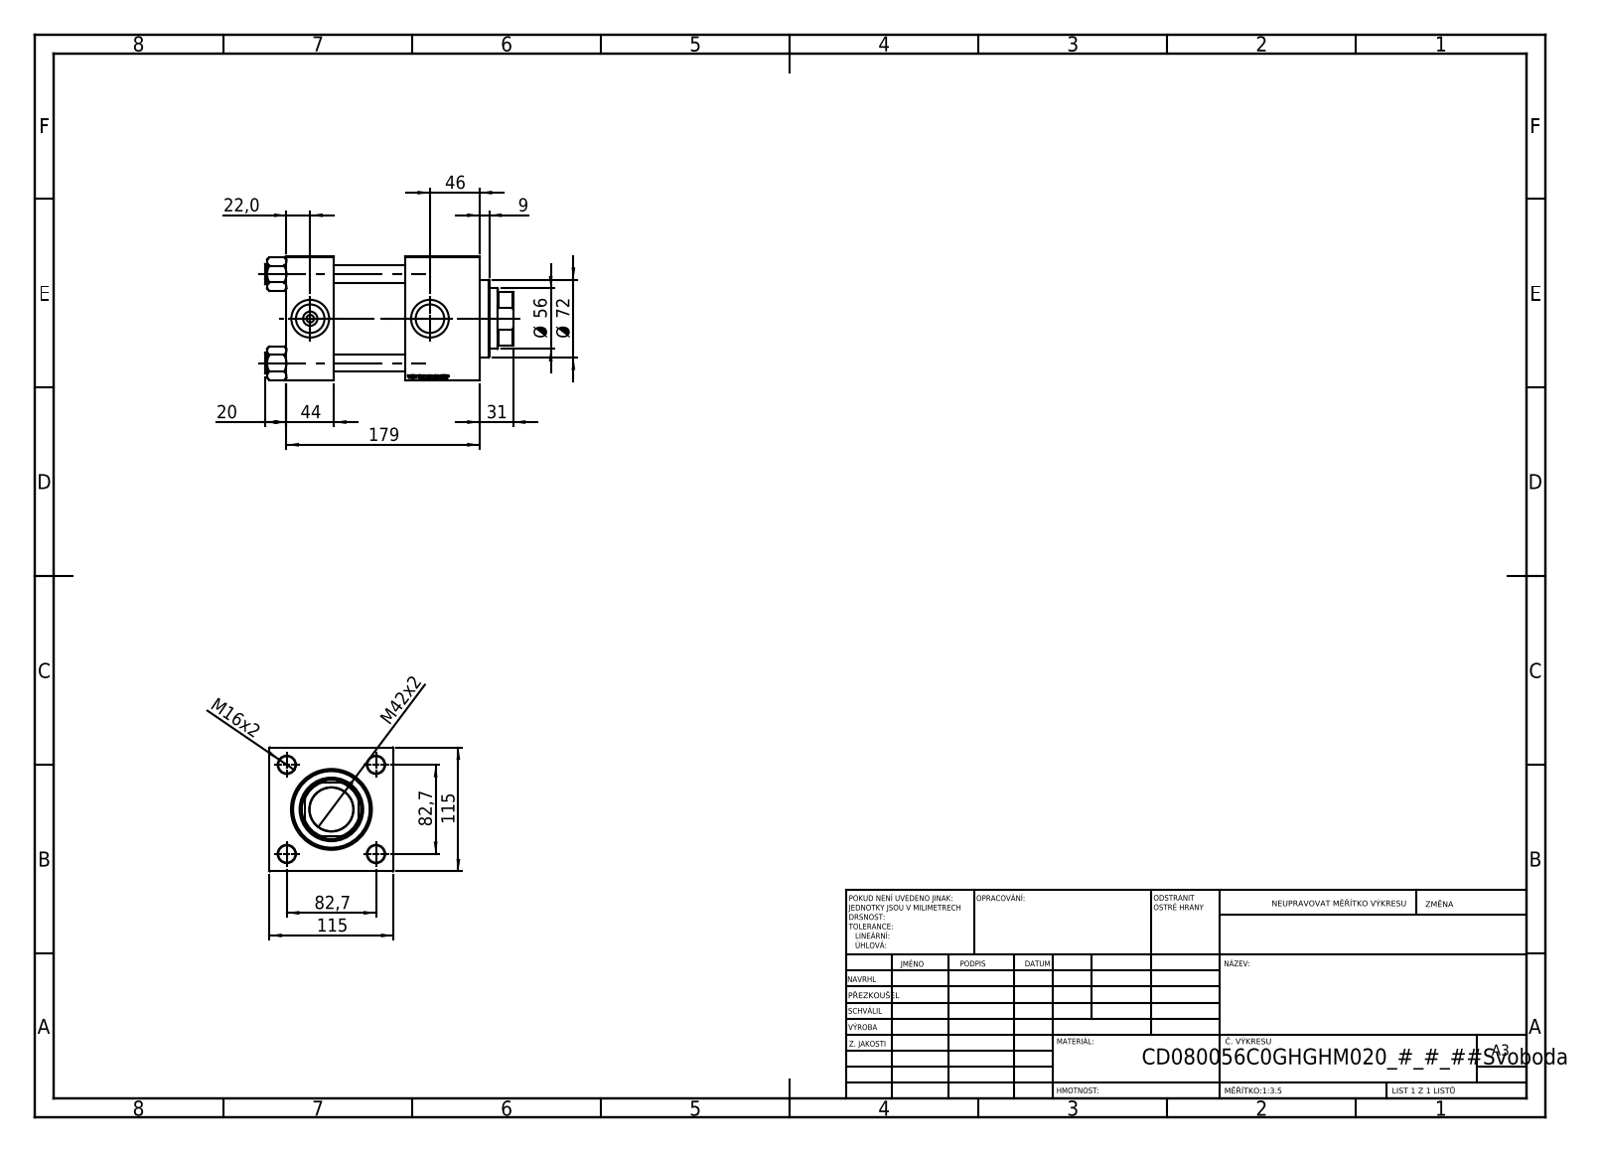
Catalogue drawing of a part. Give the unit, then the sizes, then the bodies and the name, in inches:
Units: inches
Overall size (bounding box): 9.055 × 4.528 × 4.528
Round holes (diameter × count): ⌀0.63 ×4, ⌀0.276 ×2, ⌀1.041 ×2, ⌀1.378 ×2, ⌀1.594 ×1, ⌀2.205 ×1, ⌀2.323 ×1, ⌀2.402 ×1, ⌀2.835 ×1, ⌀3.15 ×1
Round bosses / shafts (diameter × count): ⌀0.748 ×4, ⌀3.386 ×1
Partial cylindrical surfaces — rounded edges, fillets, slot ends (radius × count): R1.063 ×1
Main face-to-face distances: 4.528, 1.732, 4.331, 2.598, 7.047, 5.315, 2.717, 0.787, 5.917, 4.185
Hole centre spacings: 2.302, 3.256, 4.605, 4.37
Volume: 113.6 in³ · Surface area: 434.3 in²
Bodies: 11 solids, 1193 faces (573 planar, 84 cylindrical, 536 other)
Part name (STEP PRODUCT): V215CD_Body_C; V215CD_VC_C; V215CD_VCP_C; V215CD_C_TYCINKA (+1 more)
STEP written by: SolidWorks 2019 (CONFIG_CONTROL_DESIGN)
